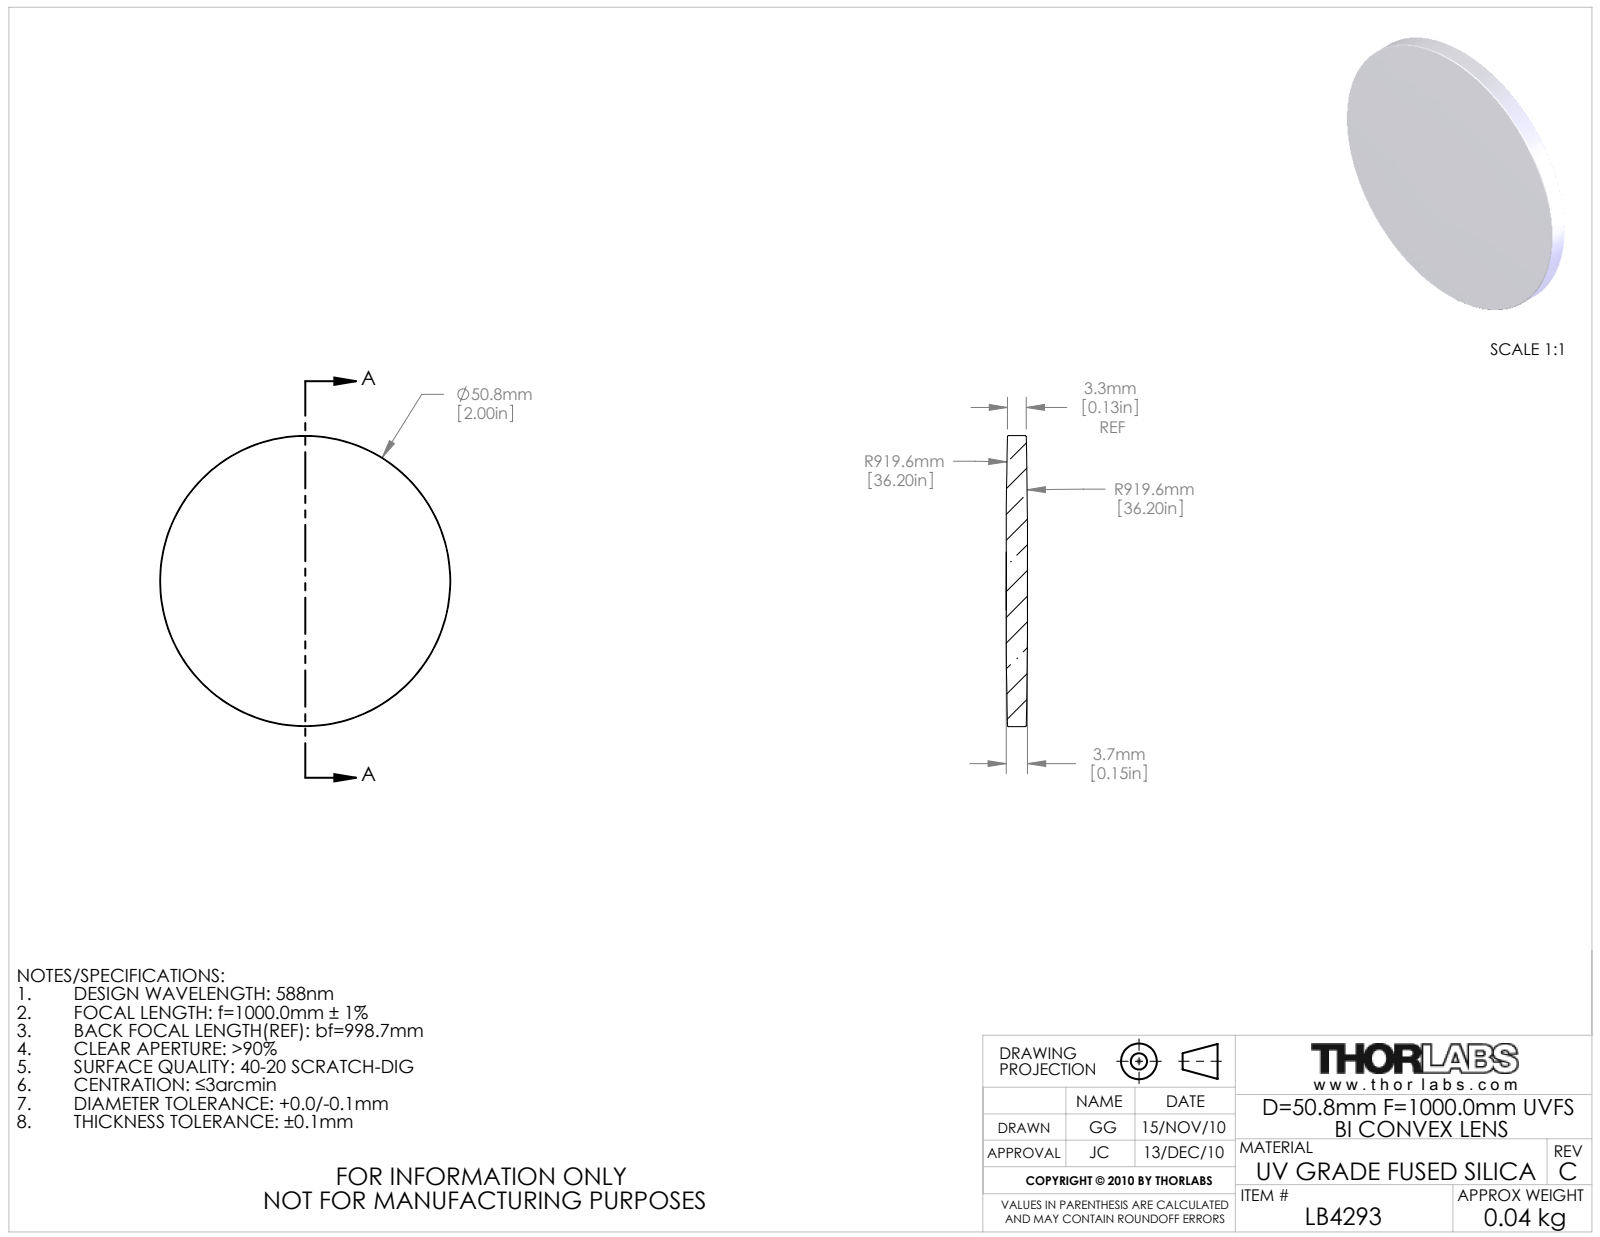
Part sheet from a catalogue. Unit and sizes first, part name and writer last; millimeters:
Units: millimetres
Overall size (bounding box): 50.8 × 50.8 × 3.73
Round bosses / shafts (diameter × count): ⌀50.8 ×1
Volume: 7 161 mm³ · Surface area: 4 552 mm²
Bodies: 1 solid, 10 faces (0 planar, 2 cylindrical, 8 other)
Part name (STEP PRODUCT): 3422-E0W
STEP written by: SolidWorks 2009 (AUTOMOTIVE_DESIGN)
